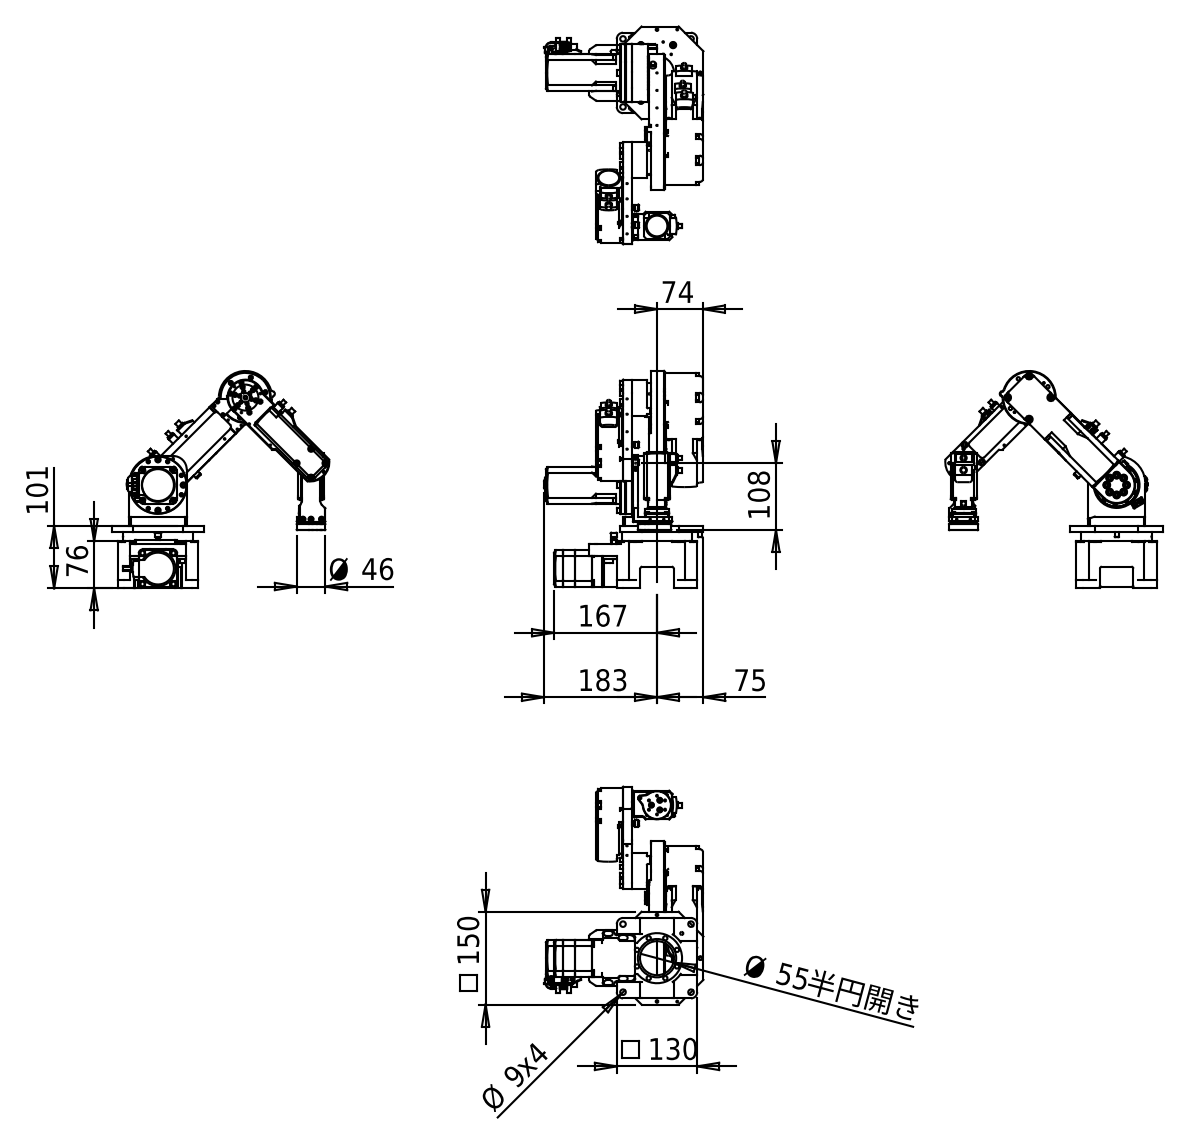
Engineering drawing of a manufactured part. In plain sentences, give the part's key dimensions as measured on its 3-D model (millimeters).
The part is named "M2_Base_01; M1_Base_01; Arm1_00; hexagon socket head cap screw2_jis_JIS B 1176 M4 x 12 (12) --N (+7 more)". Its 3-D file was written by "SolidWorks 2020 (AUTOMOTIVE_DESIGN)". It is 12 solids with 6128 faces: 2538 planar, 1931 cylindrical and 1659 other. Overall it measures 352.07 by 351.42 by 257.9 millimeters. Its volume is 3 661 000 cubic millimeters and its surface area 568 832 square millimeters. Round holes: 52 of diameter 2.5, 31 of diameter 4.2, 25 of diameter 3.3, 20 of diameter 5.5, 16 of diameter 10, 12 of diameter 4.8, 11 of diameter 4.5, 8 of diameter 2, 8 of diameter 6.5, 8 of diameter 6.6, 8 of diameter 8, 8 of diameter 11. Round bosses or shafts: 60 of diameter 7, 22 of diameter 4, 20 of diameter 5.5, 18 of diameter 10, 14 of diameter 8.5, 14 of diameter 6, 10 of diameter 5.68, 10 of diameter 5. Partial cylindrical surfaces (rounded edges, fillets, slot ends): 41 of radius 1, 36 of radius 0.2, 29 of radius 1.5, 24 of radius 4, 23 of radius 2.62, 23 of radius 2.64, 18 of radius 2, 17 of radius 5.3. The main face-to-face distances are 10, 15, 53, 60, 2, 25, 46, 1.5, 26.5, 35. The hole center spacings are 52, 41, 31.38, 57.98, 75.76, 25, 55.57, 70.
